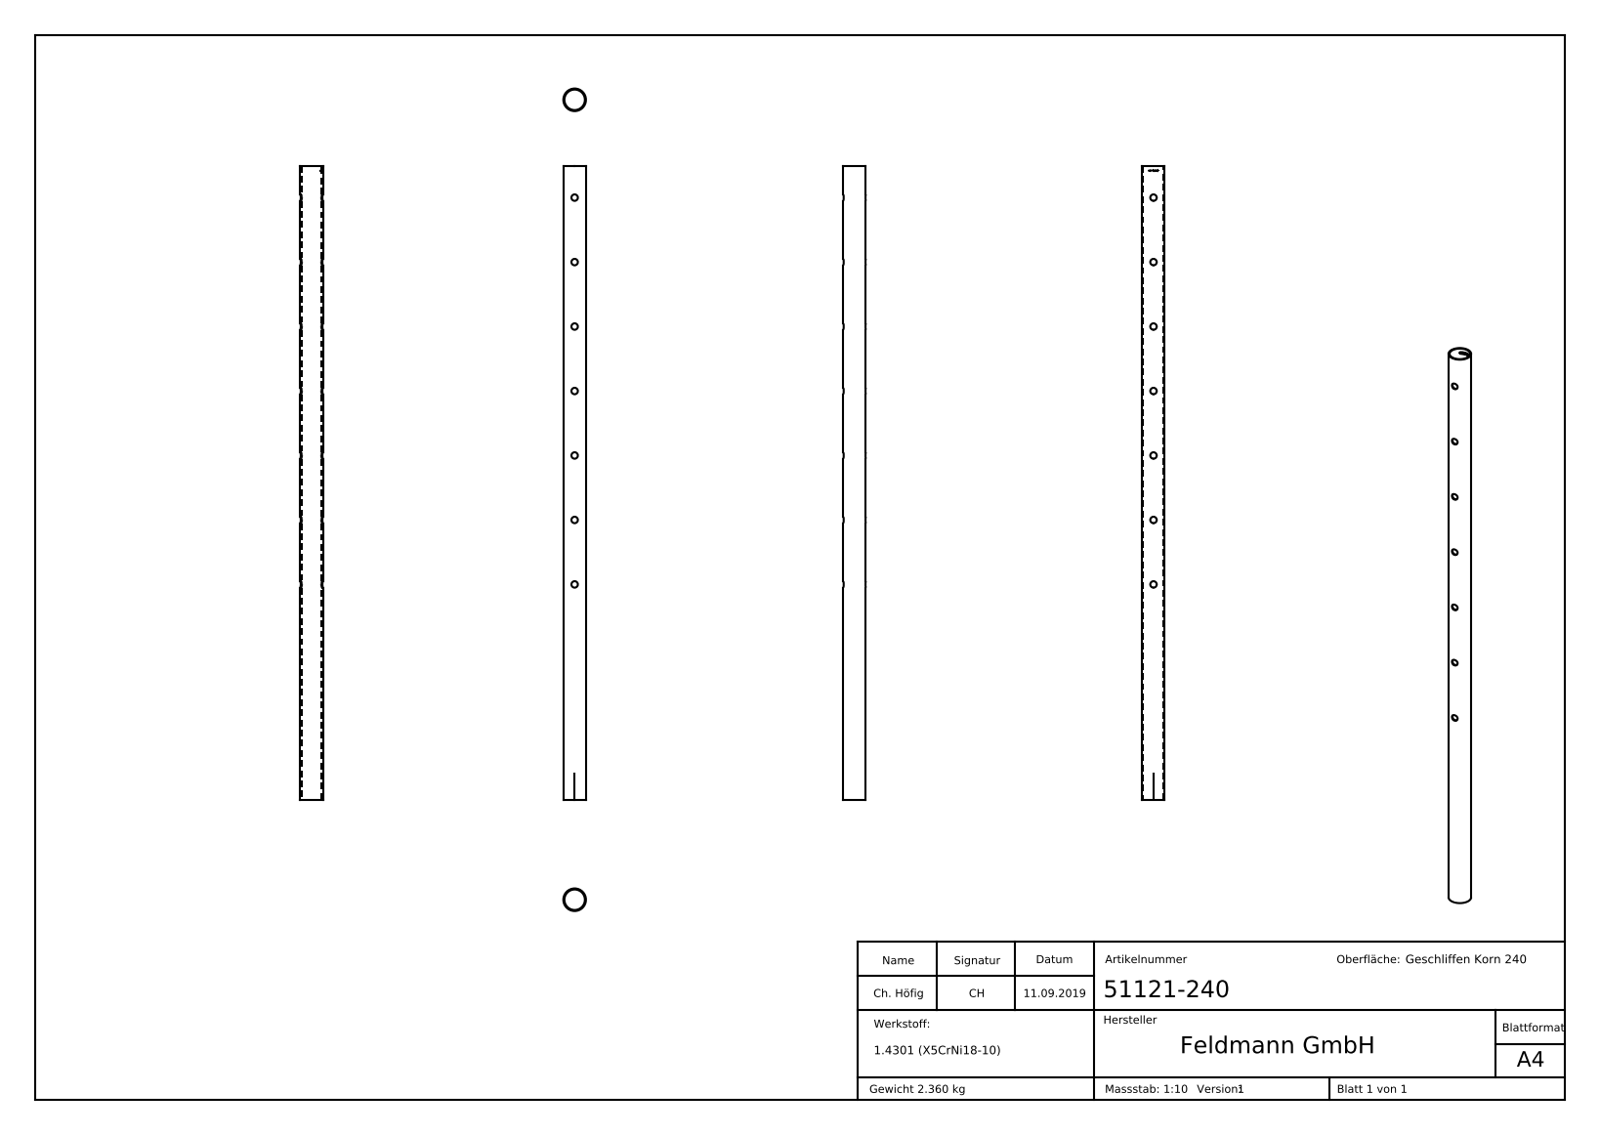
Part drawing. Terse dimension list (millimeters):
name: 51121-240
written by: SolidWorks 2015 (CONFIG_CONTROL_DESIGN)
unit: mm
bodies: 1 solid, 240 faces (109 planar, 54 cylindrical, 77 other)
size: 1190 × 42.4 × 42.4
volume: 298 812 mm³; area: 300 420 mm²
holes: 7× ⌀12.1, 1× ⌀38.4
bosses: 1× ⌀42.4
rounds: 1× R19.3
face distances: 1190, 1180, 10, 1.01, 2.04, 2.97, 0.44, 1.32, 3.05, 13.77
hole spacings: 121, 242, 363, 484, 605, 726
